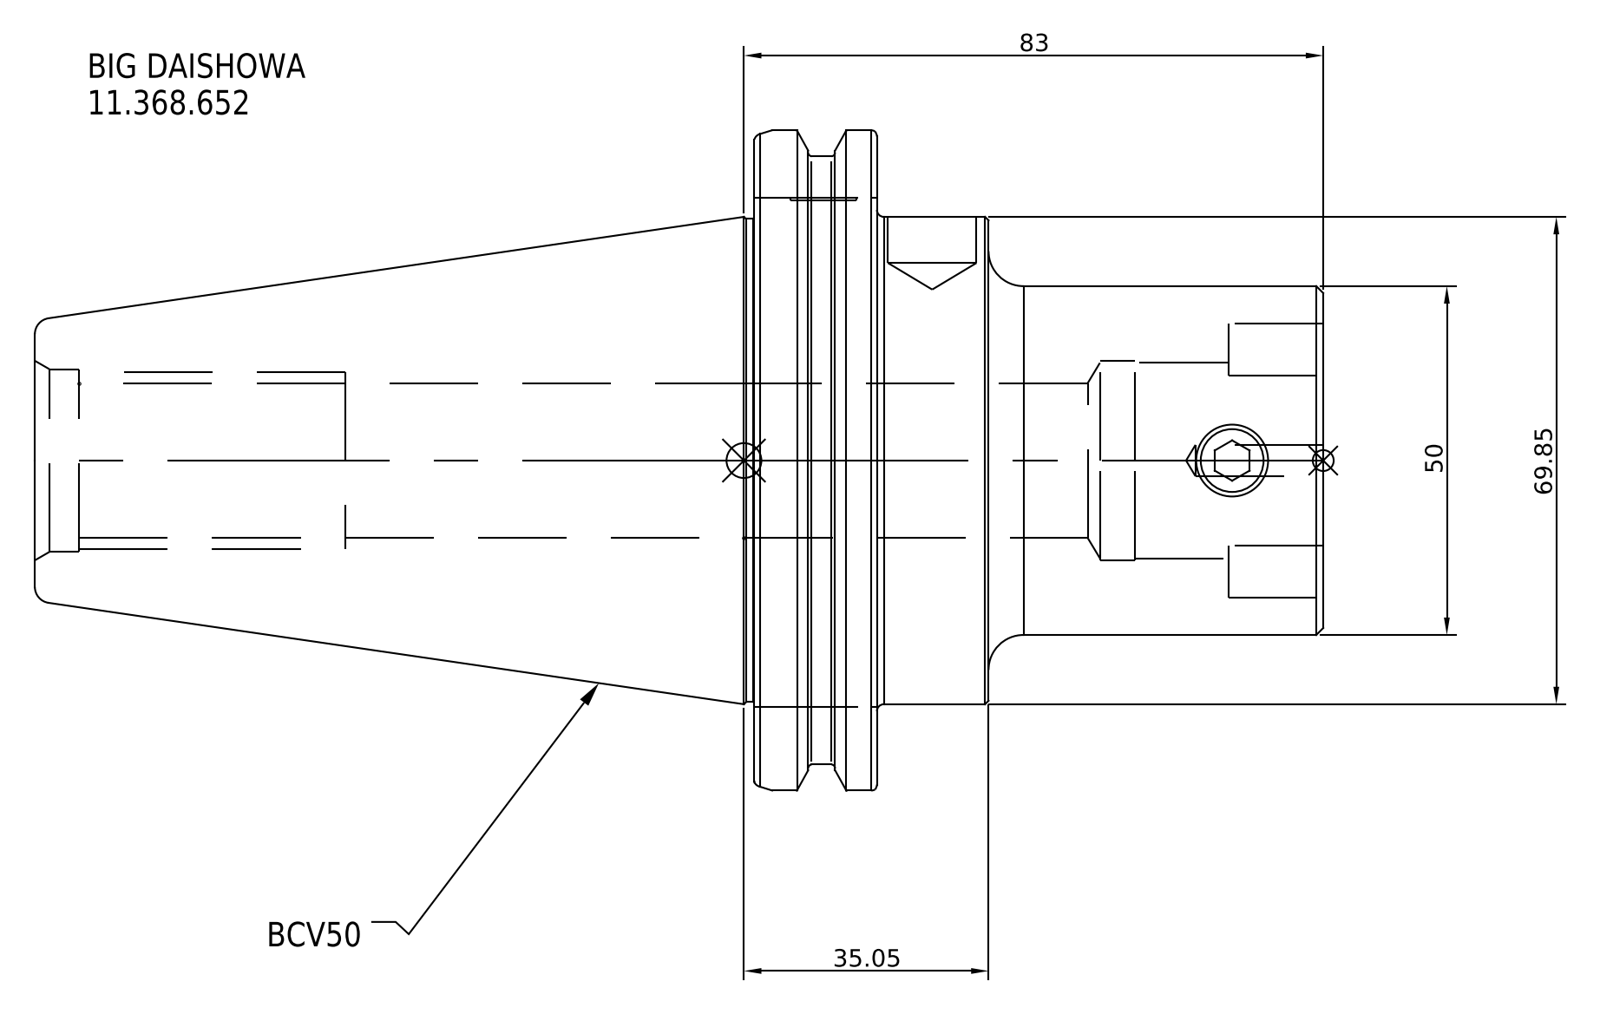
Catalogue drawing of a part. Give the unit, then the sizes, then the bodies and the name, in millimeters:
Units: millimetres
Overall size (bounding box): 184.6 × 98.43 × 98.43
Round bosses / shafts (diameter × count): ⌀98.43 ×1, ⌀91.29 ×1, ⌀69.85 ×1, ⌀50 ×1
Main face-to-face distances: 17.55, 63.95, 81.5, 48, 15.95, 33.5, 184.6, 136.6, 120.65, 103.1
Volume: 536 728 mm³ · Surface area: 48 513 mm²
Bodies: 1 solid, 16 faces (7 planar, 6 cylindrical, 3 other)
Part name (STEP PRODUCT): 11.368.652
STEP written by: SolidWorks 2021 (CONFIG_CONTROL_DESIGN)
